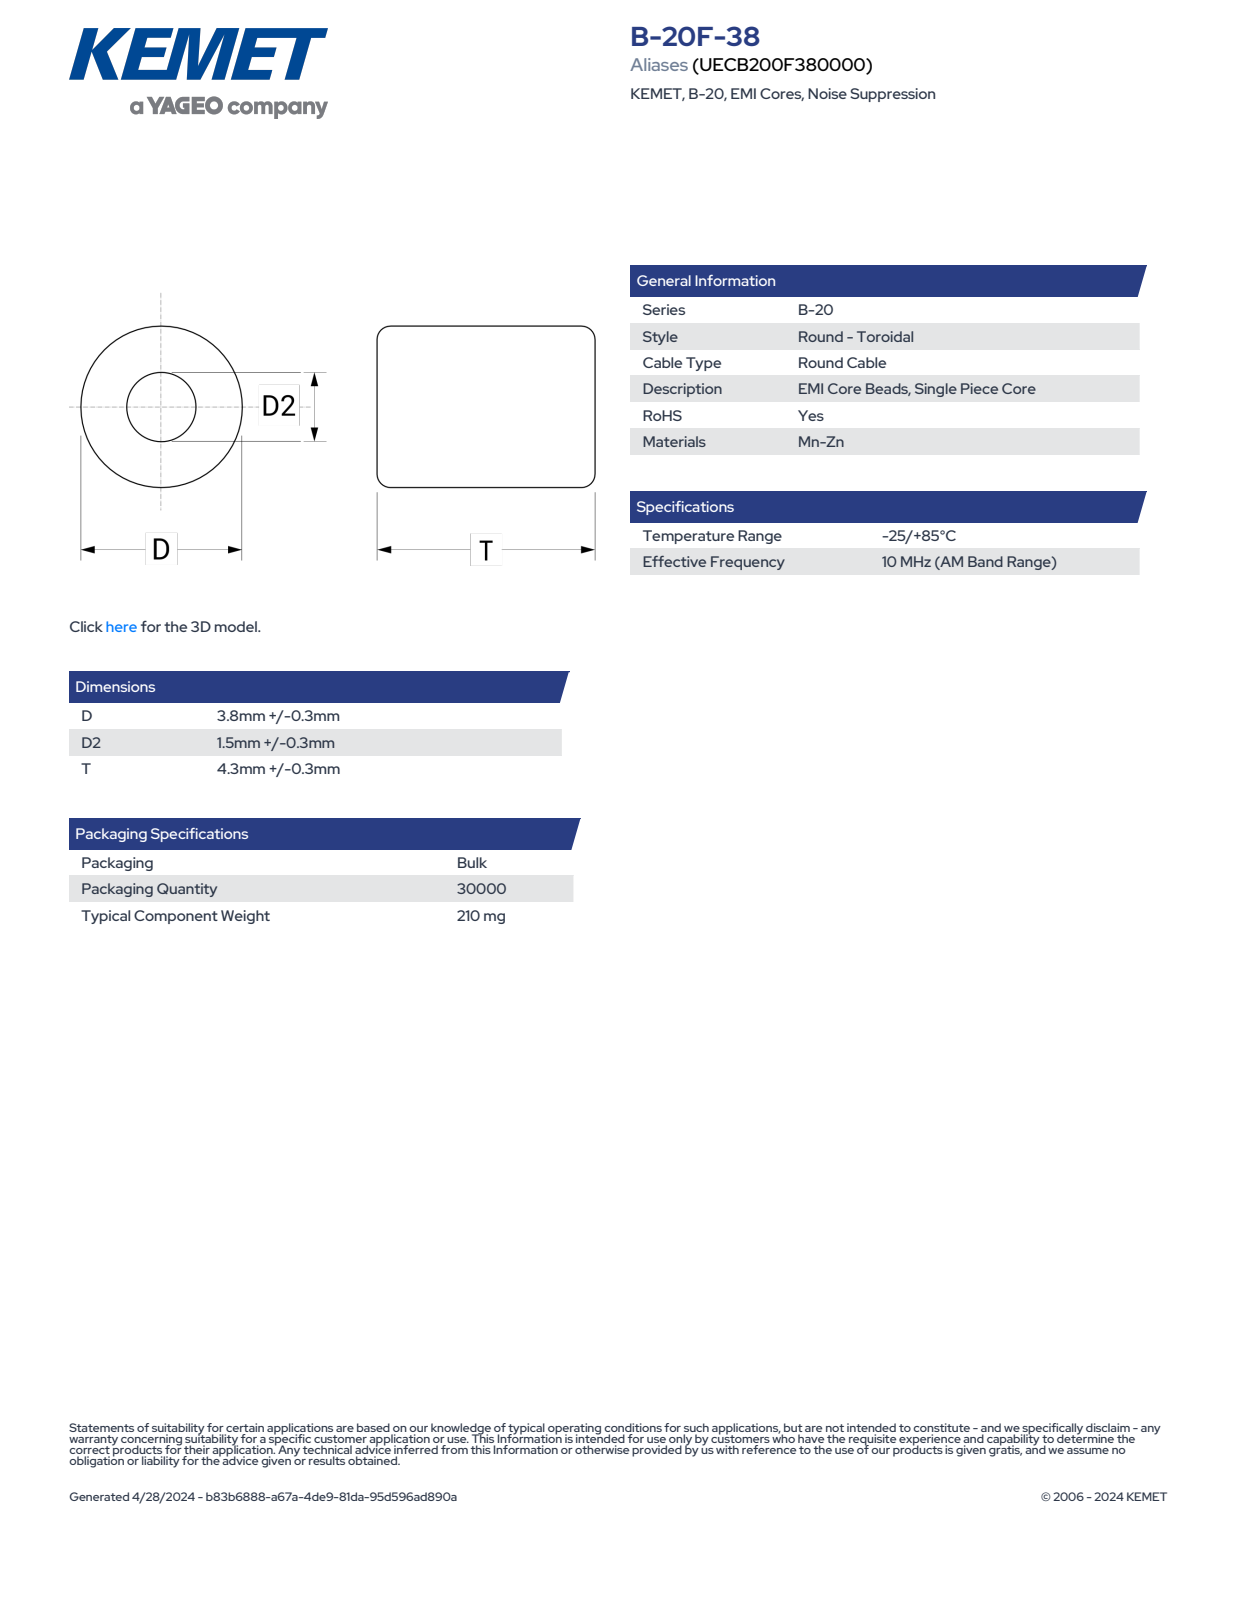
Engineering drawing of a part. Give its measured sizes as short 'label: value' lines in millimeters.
name: EC_KBCH_D4.1D21.5T4.6
written by: SolidWorks 2021 (AUTOMOTIVE_DESIGN)
unit: mm
bodies: 1 solid, 66 faces (25 planar, 7 cylindrical, 34 other)
size: 4.6 × 4.11 × 4.1
volume: 53 mm³; area: 103 mm²
holes: 1× ⌀1.5
bosses: 1× ⌀4.1
rounds: 1× R2.06
face distances: 4.6, 2.11, 2.49, 0.38, 2.18, 2.42, 0.31, 2.35, 2.25, 2.28
